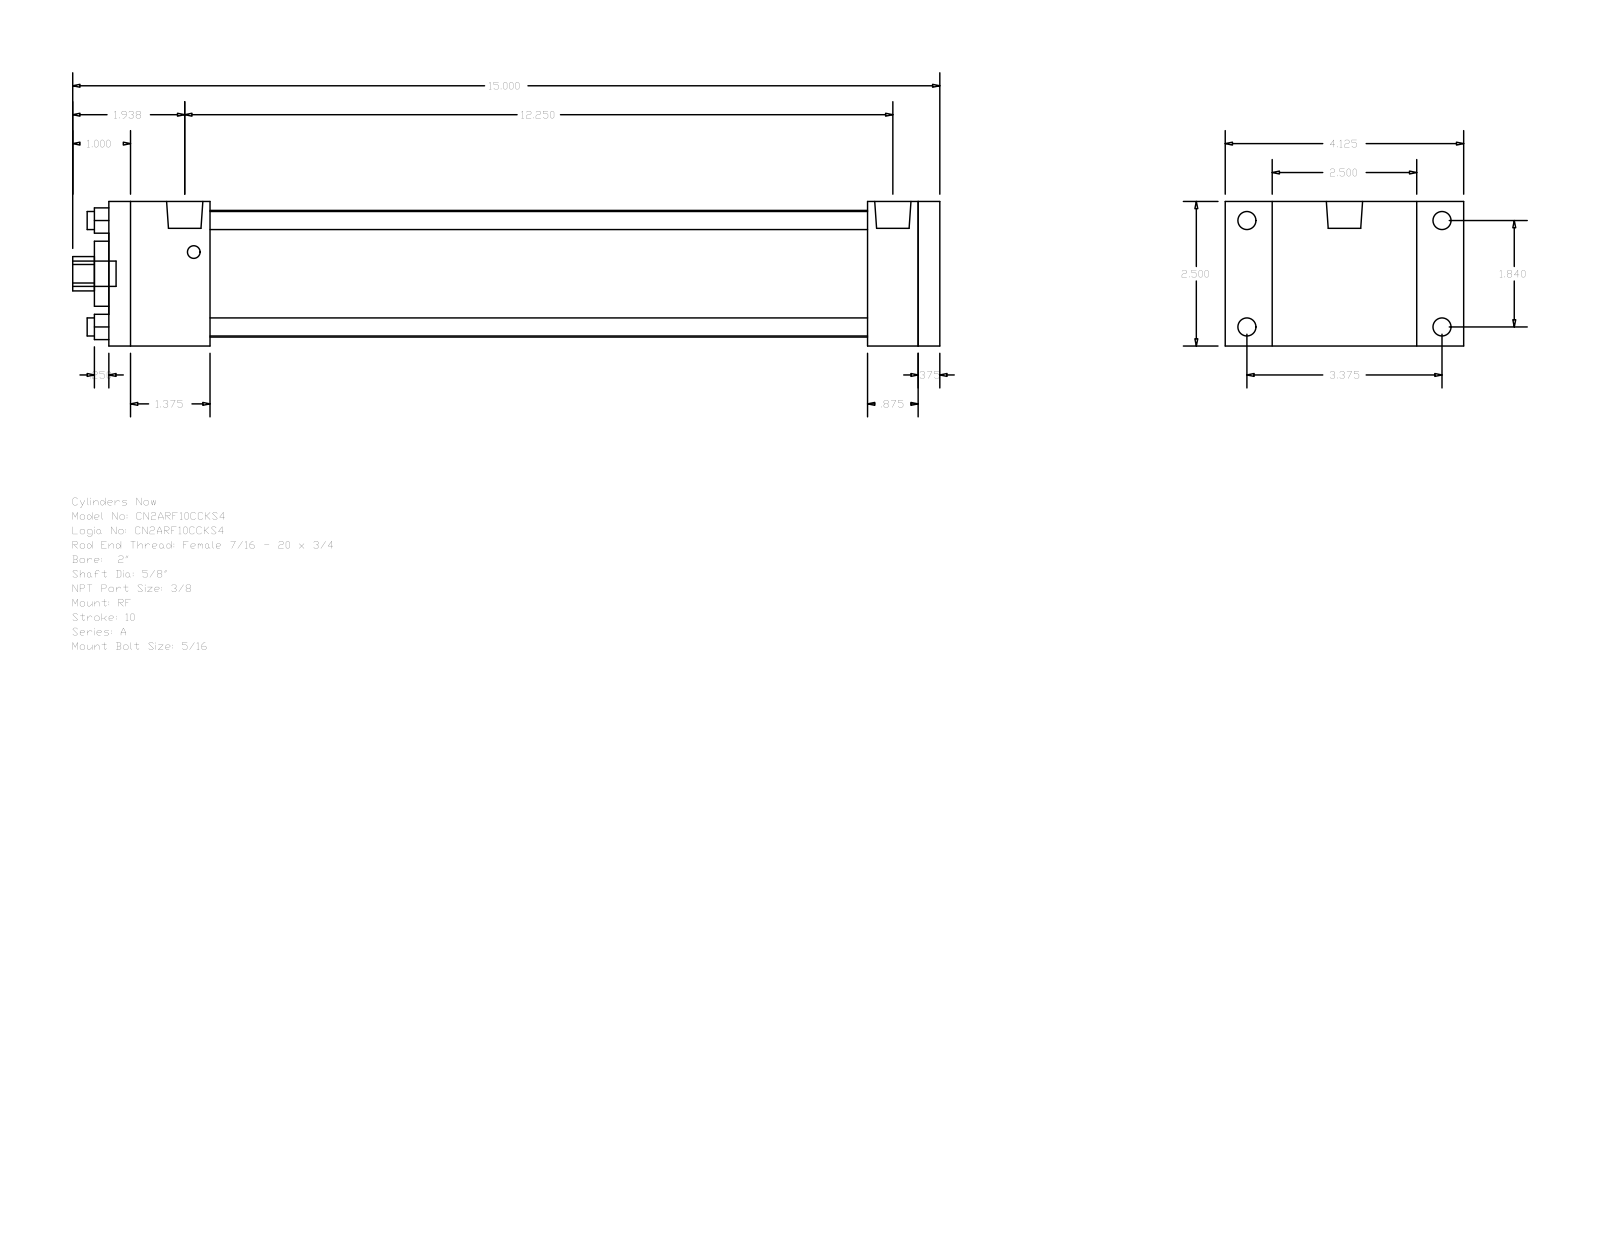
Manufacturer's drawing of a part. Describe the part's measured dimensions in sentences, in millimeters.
The part is named "A_RF__0200_0.625". Its 3-D file was written by "GSSL Pune (CONFIG_CONTROL_DESIGN)". It is 0 solids with 92 faces: 64 planar, 28 cylindrical and 0 other. Overall it measures 381 by 104.78 by 63.5 millimeters. Round holes: 4 of diameter 7.94, 1 of diameter 15.88, 1 of diameter 28.57, 1 of diameter 55.63. Round bosses or shafts: 4 of diameter 7.94, 4 of diameter 5.56, 2 of diameter 15.93, 1 of diameter 11.11. Partial cylindrical surfaces (rounded edges, fillets, slot ends): 1 of radius 7.54. The main face-to-face distances are 63.5, 365.12, 9.52, 355.6, 44.45, 311.15, 320.67, 333.37, 288.92, 22.23. The hole center spacings are 33.05, 46.74, 66.1.
